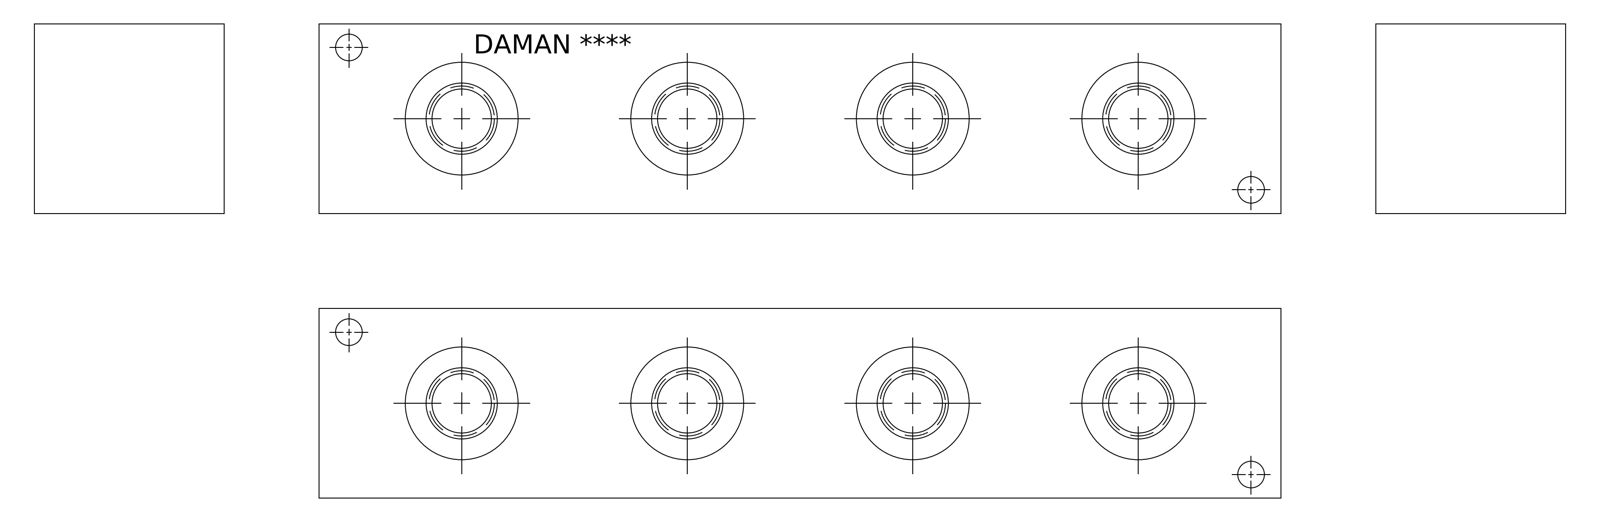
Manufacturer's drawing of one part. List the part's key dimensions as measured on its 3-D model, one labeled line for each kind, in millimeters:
Part name (STEP PRODUCT): Part_AJ0900408S_3D
STEP written by: Autodesk Inventor 2019 (AUTOMOTIVE_DESIGN)
Units: millimetres
Bodies: 1 solid, 417 faces (222 planar, 48 cylindrical, 147 other)
Overall size (bounding box): 257.18 × 50.8 × 50.8
Volume: 603 994 mm³ · Surface area: 70 737 mm²
Round holes (diameter × count): ⌀15.88 ×8, ⌀17.5 ×8, ⌀19.05 ×8, ⌀19.25 ×8, ⌀30.63 ×8, ⌀7.14 ×4
Main face-to-face distances: 50.8, 50.01, 0.79, 257.18, 35.74, 14.27, 15.06, 49.8, 14.06, 1
Hole centre spacings: 60.32, 120.65, 35.66, 35.69, 60.33, 92.45, 92.48, 152
